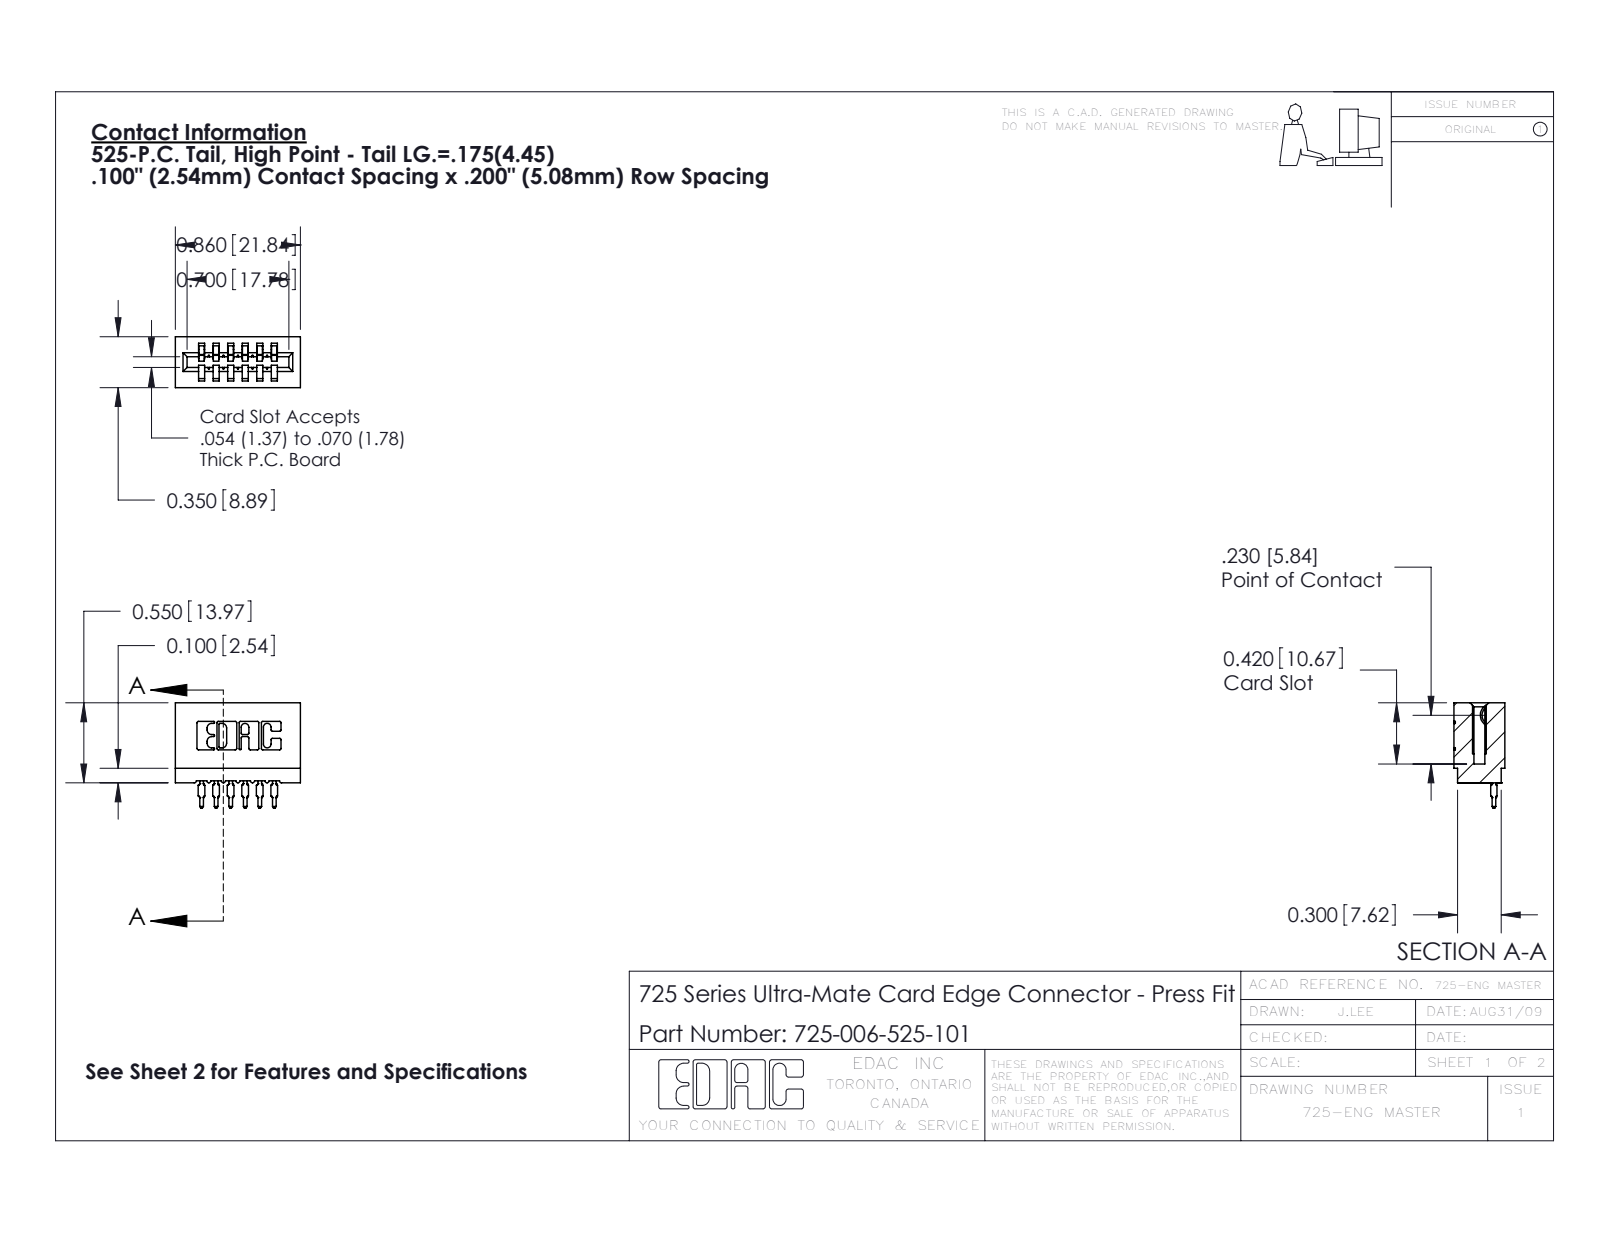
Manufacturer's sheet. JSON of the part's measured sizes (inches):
{"part_name": "725 Part_Insulator Option - 01; 725-006-525-101; 745-292-001_525", "step_written_by": "SolidWorks 2016 (CONFIG_CONTROL_DESIGN)", "units": "inches", "bodies": {"solids": 7, "faces": 767, "planar": 457, "cylindrical": 154, "other": 156}, "overall_size": [0.86, 0.725, 0.35], "volume_in3": 0.113, "surface_area_in2": 4.491, "partial_cylinders_radius": [[0.01, 22], [0.015, 12], [0.021, 12], [0.007, 6], [0.031, 6], [0.005, 4], [0.011, 4], [0.026, 3]], "face_to_face_distances": [0.1, 0.2, 0.042, 0.3, 0.058, 0.142, 0.158, 0.242, 0.4, 0.35]}
